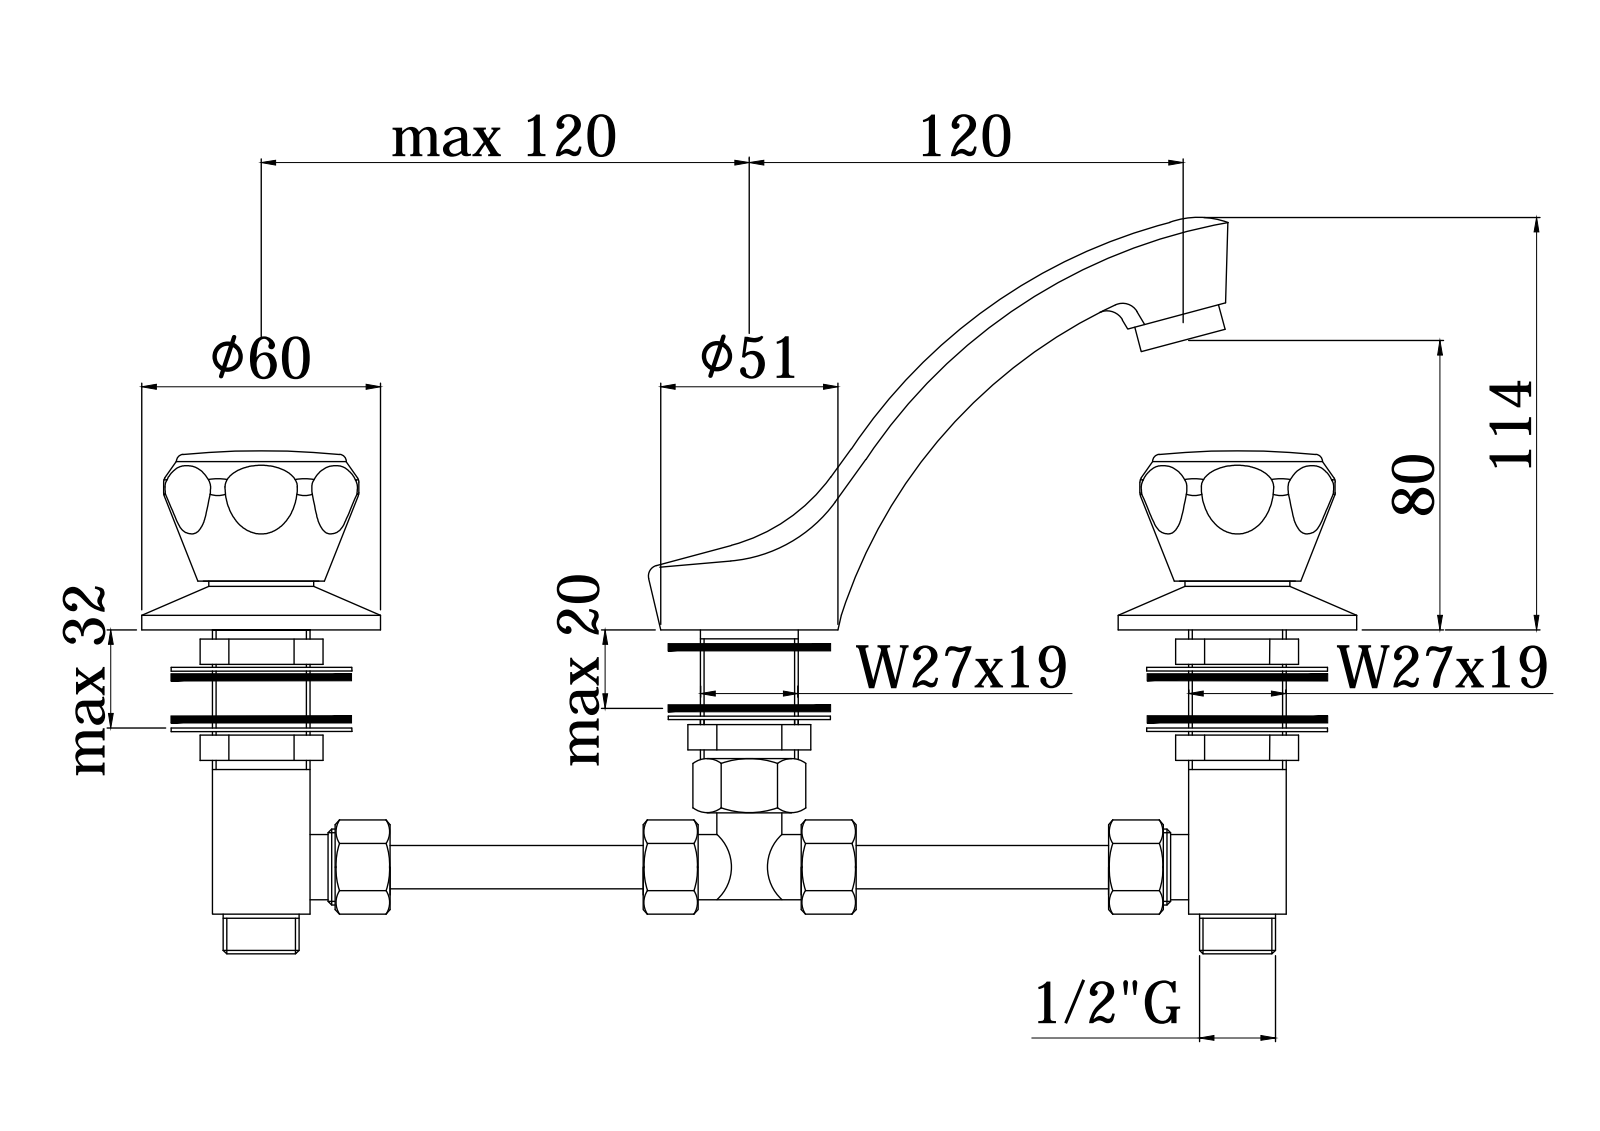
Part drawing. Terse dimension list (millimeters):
name: DA053CR
written by: CREO PARAMETRIC BY PTC INC, 2020044 (CONFIG_CONTROL_DESIGN)
unit: mm
bodies: 3 solids, 324 faces (45 planar, 62 cylindrical, 217 other)
size: 262 × 164.44 × 123.29
volume: 261 779 mm³; area: 74 658 mm²
holes: 2× ⌀5, 2× ⌀9, 2× ⌀11, 1× ⌀16, 1× ⌀21, 1× ⌀23, 1× ⌀42, 1× ⌀48
bosses: 2× ⌀62, 2× ⌀38.5, 1× ⌀23.8, 1× ⌀22, 1× ⌀8, 1× ⌀4.5
rounds: 16× R21.31, 4× R1.5, 2× R5, 2× R7.5
face distances: 3, 2, 4, 13.8, 6, 49.1, 35.3, 9.8, 45.1, 49.5
hole spacings: 9.6, 14.21, 15.4, 23.82, 15, 22
